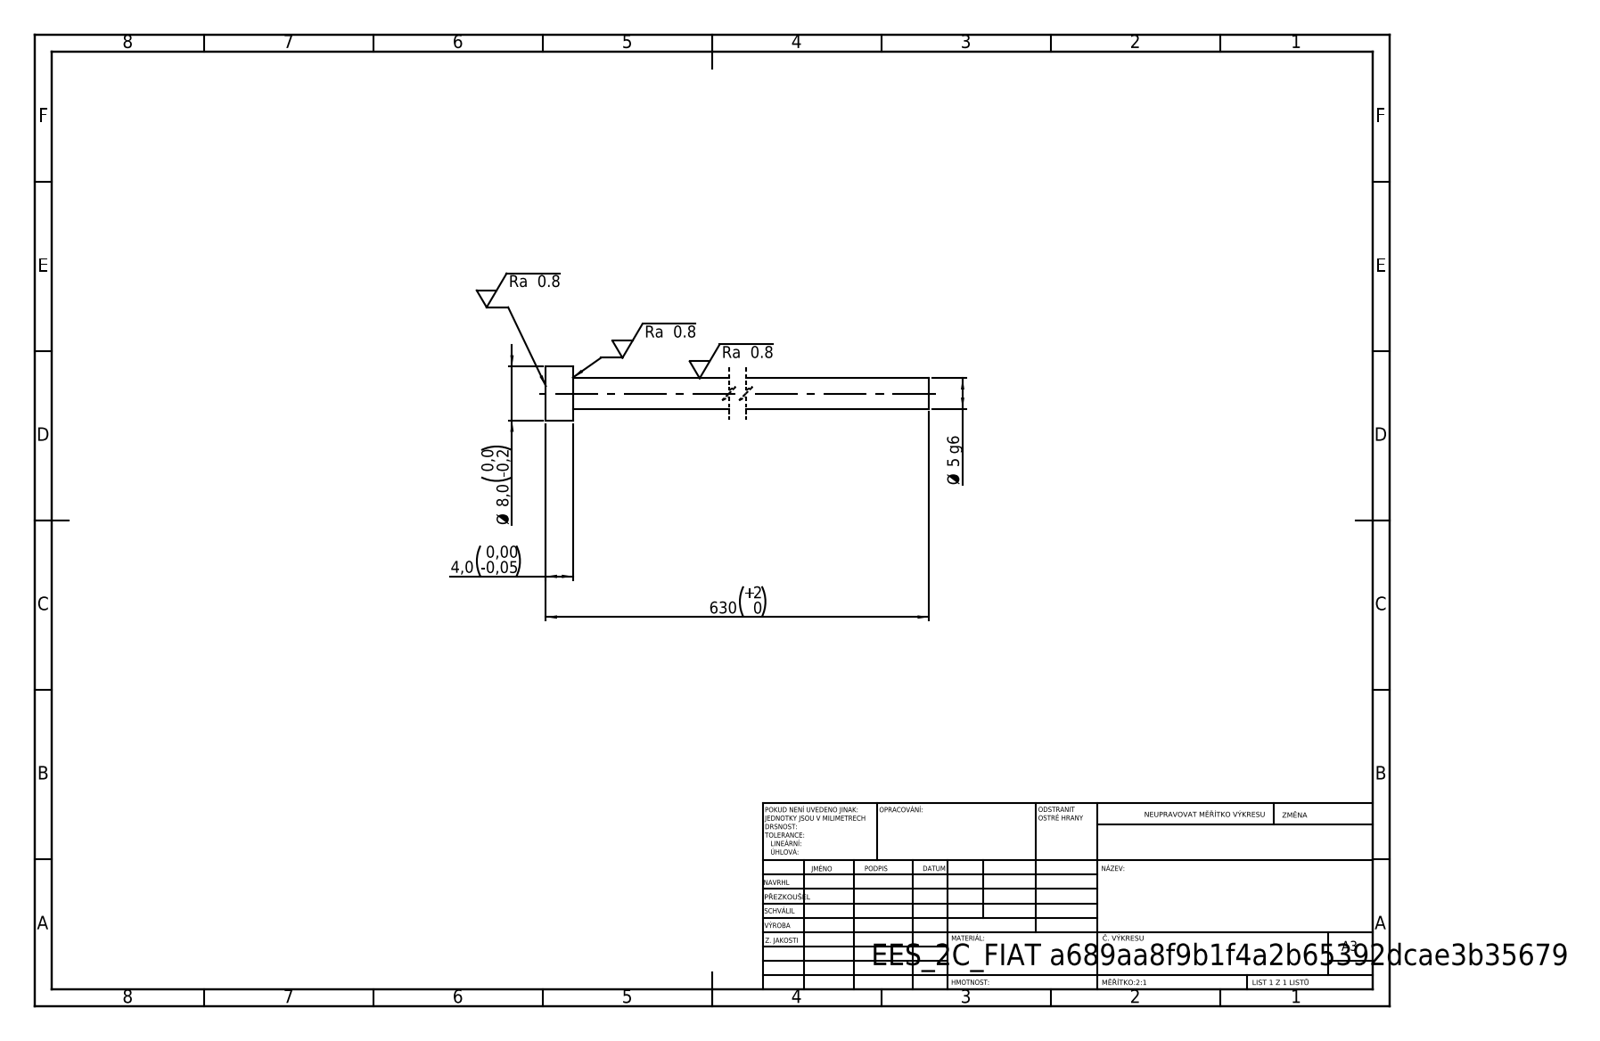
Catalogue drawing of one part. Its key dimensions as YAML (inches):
step_written_by: "SolidWorks 2019 (CONFIG_CONTROL_DESIGN)"
units: inches
bodies: {solids: 1, faces: 7, planar: 3, cylindrical: 4, other: 0}
overall_size: [24.803, 0.315, 0.315]
volume: 0.62
surface_area: 14.03
round_bosses_or_shafts:
  - {diameter: 0.315, count: 1}
  - {diameter: 0.177, count: 1}
face_to_face_distances: [0.157, 24.803, 24.646]
